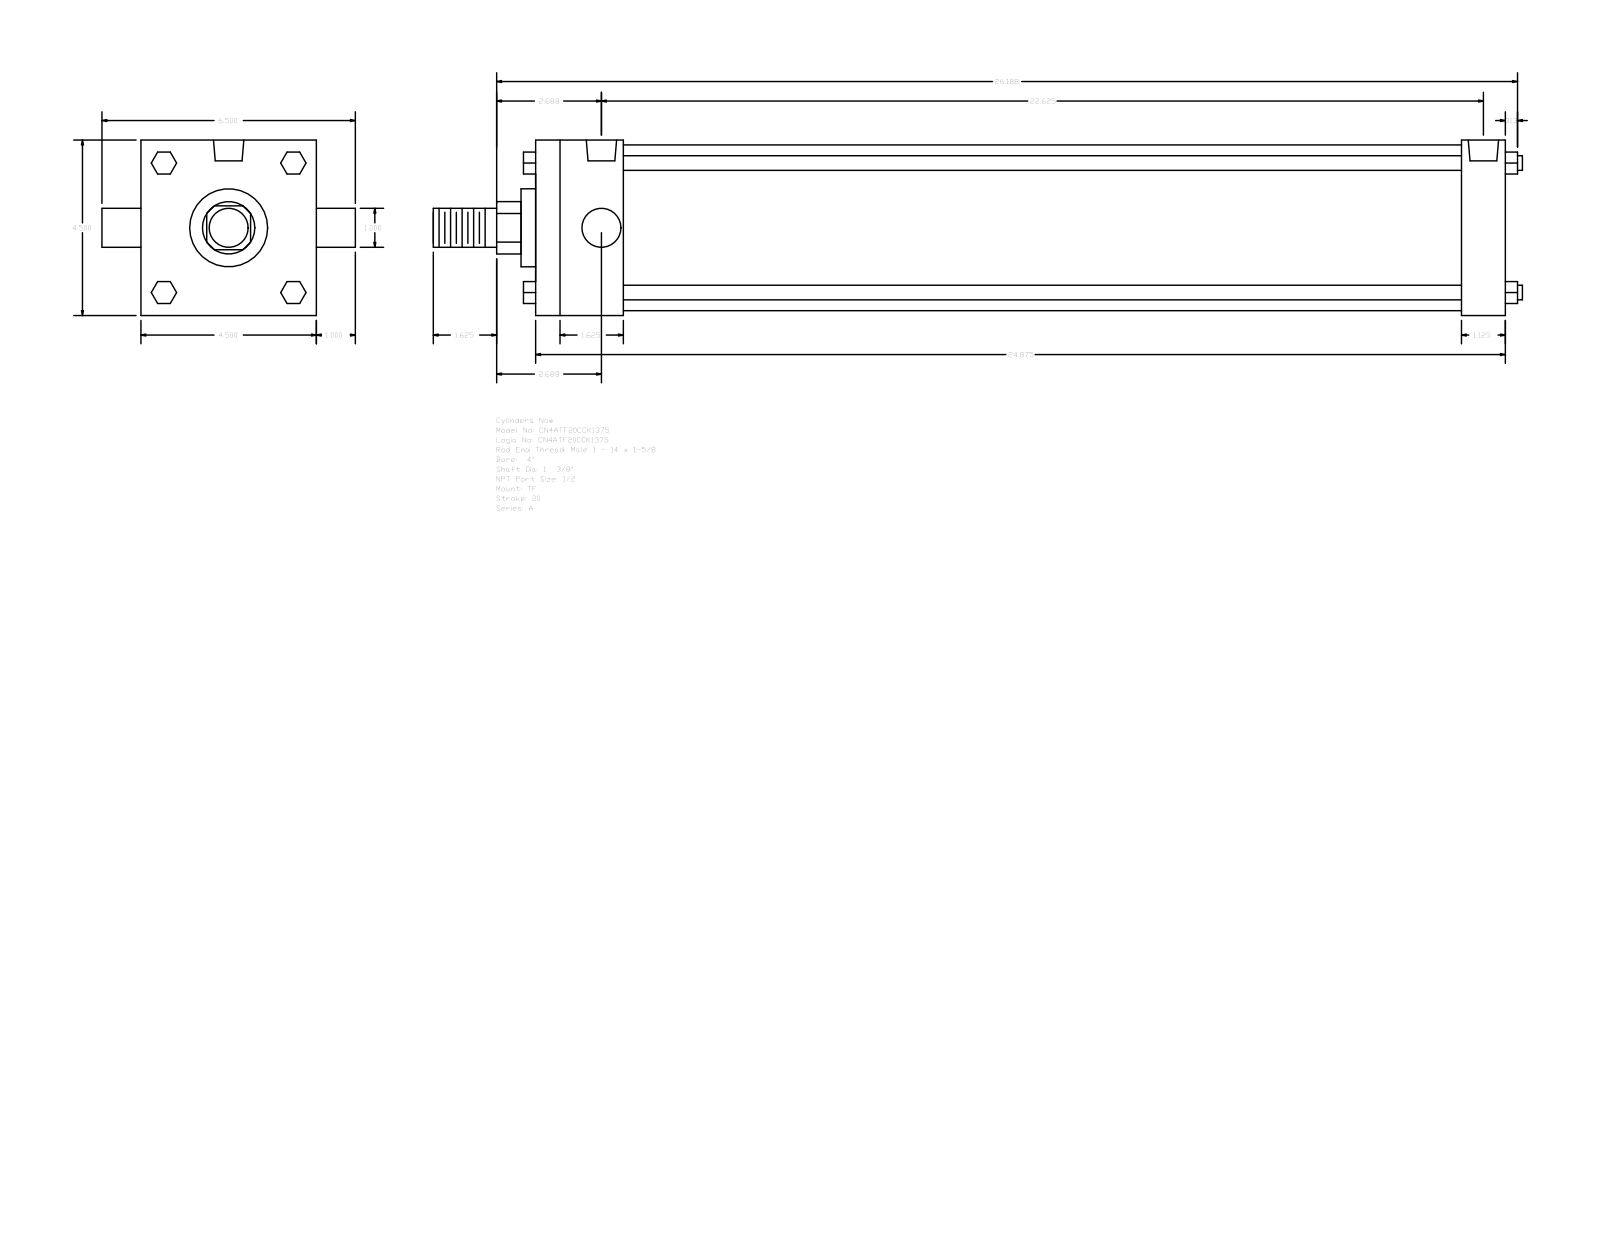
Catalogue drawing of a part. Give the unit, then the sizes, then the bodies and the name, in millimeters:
Units: millimetres
Overall size (bounding box): 709.61 × 165.1 × 114.3
Round holes (diameter × count): ⌀8.73 ×3, ⌀19.77 ×2
Round bosses / shafts (diameter × count): ⌀9.53 ×4, ⌀25.4 ×2, ⌀107.95 ×1, ⌀50.8 ×1, ⌀34.92 ×1
Partial cylindrical surfaces — rounded edges, fillets, slot ends (radius × count): R17.06 ×1
Main face-to-face distances: 114.3, 631.83, 57.15, 28.58, 603.25, 546.1, 574.68, 66.67, 14.29, 25.4
Hole centre spacings: 3.18, 571.5, 568.32, 574.68
Bodies: 0 solids, 120 faces (92 planar, 28 cylindrical, 0 other)
Part name (STEP PRODUCT): A_TF__0400_1.375
STEP written by: GSSL Pune (CONFIG_CONTROL_DESIGN)
